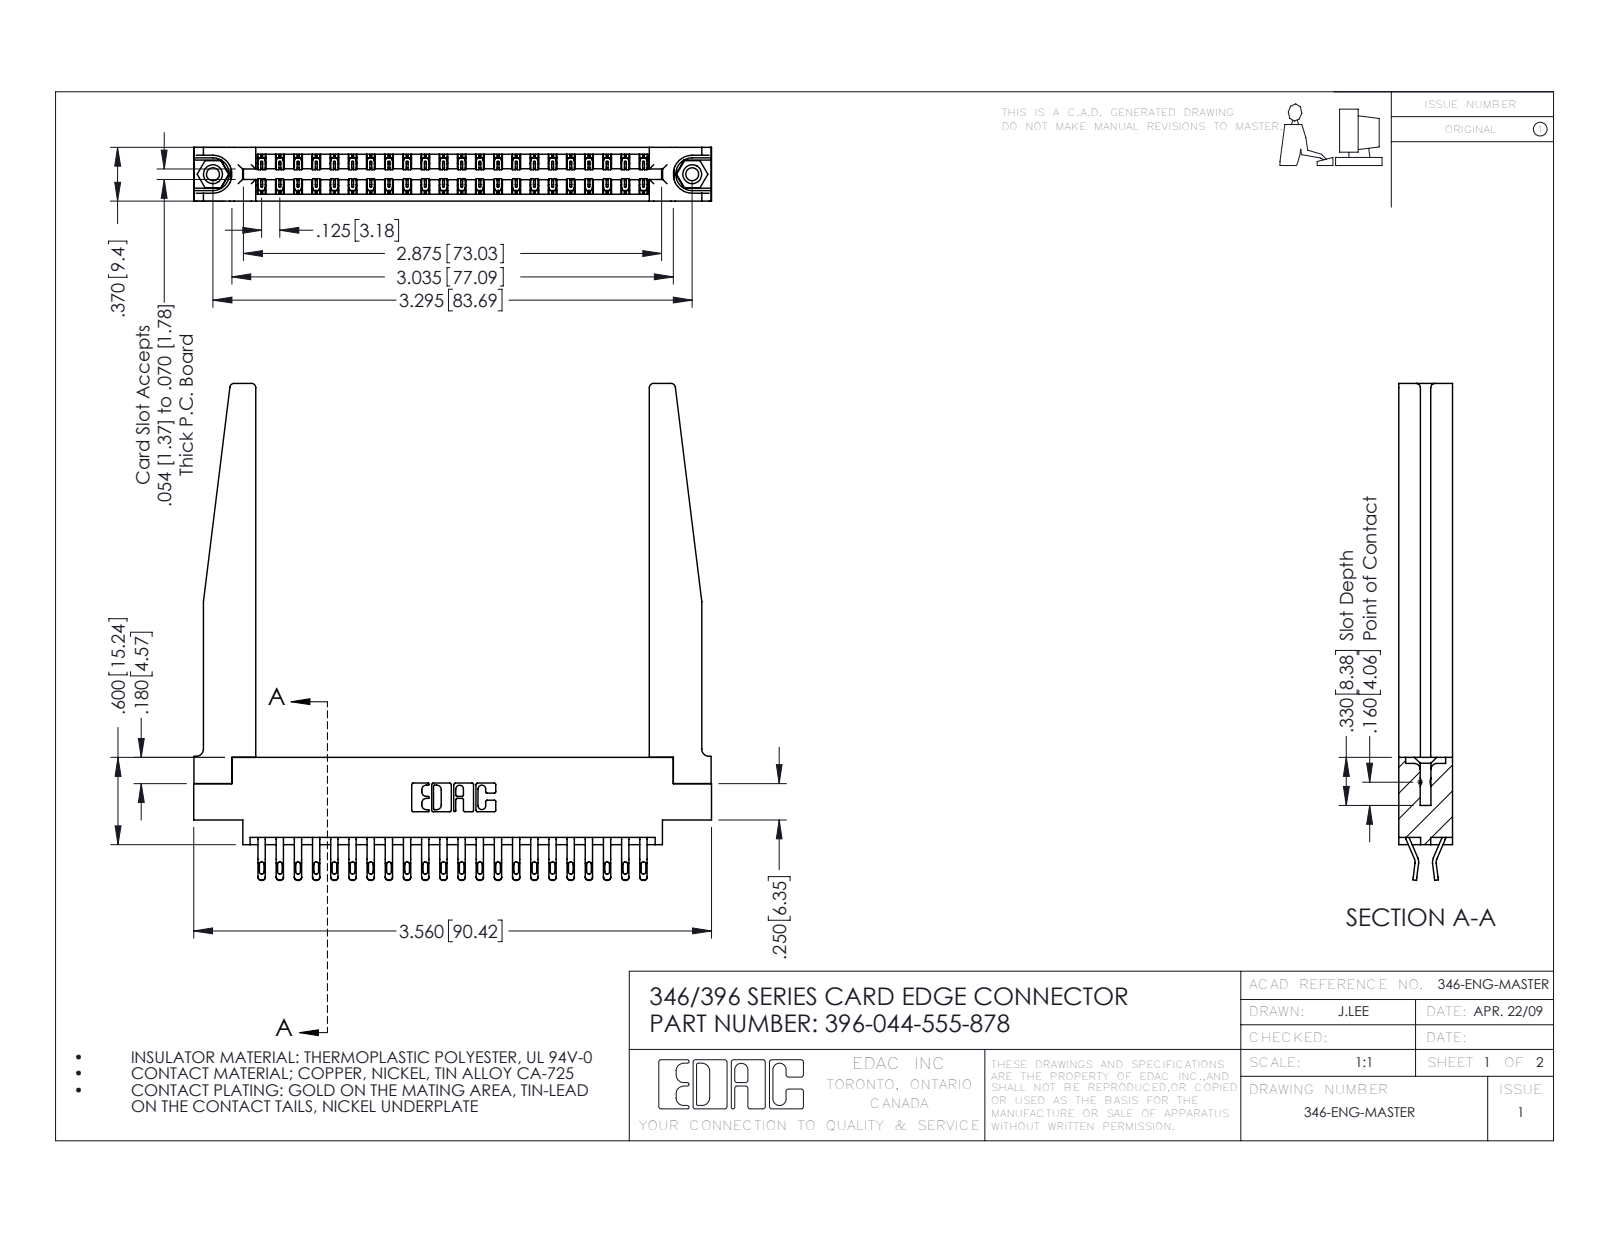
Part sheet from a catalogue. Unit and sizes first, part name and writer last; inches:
Units: inches
Overall size (bounding box): 3.56 × 3.415 × 0.37
Round holes (diameter × count): ⌀0.089 ×2, ⌀0.125 ×2, ⌀0.156 ×2, ⌀0.064 ×1
Round bosses / shafts (diameter × count): ⌀0.155 ×2
Partial cylindrical surfaces — rounded edges, fillets, slot ends (radius × count): R0.016 ×88, R0.02 ×88, R0.006 ×66, R0.01 ×22, R0.03 ×8, R0.007 ×6, R0.031 ×6, R0.05 ×4
Main face-to-face distances: 0.37, 0.048, 0.322, 0.072, 0.148, 0.15, 0.25, 0.025, 0.298, 0.275
Hole centre spacings: 0.246, 3.087, 3.295
Volume: 0.949 in³ · Surface area: 29.03 in²
Bodies: 49 solids, 2912 faces (1674 planar, 1186 cylindrical, 52 other)
Part name (STEP PRODUCT): 346 Part_0.170 Offset - 0.156 Dia-TH; 346-220-078_345-220-078; 345-250-001_345-250-001-102; 396-044-555-878 (+1 more)
STEP written by: SolidWorks 2016 (CONFIG_CONTROL_DESIGN)
